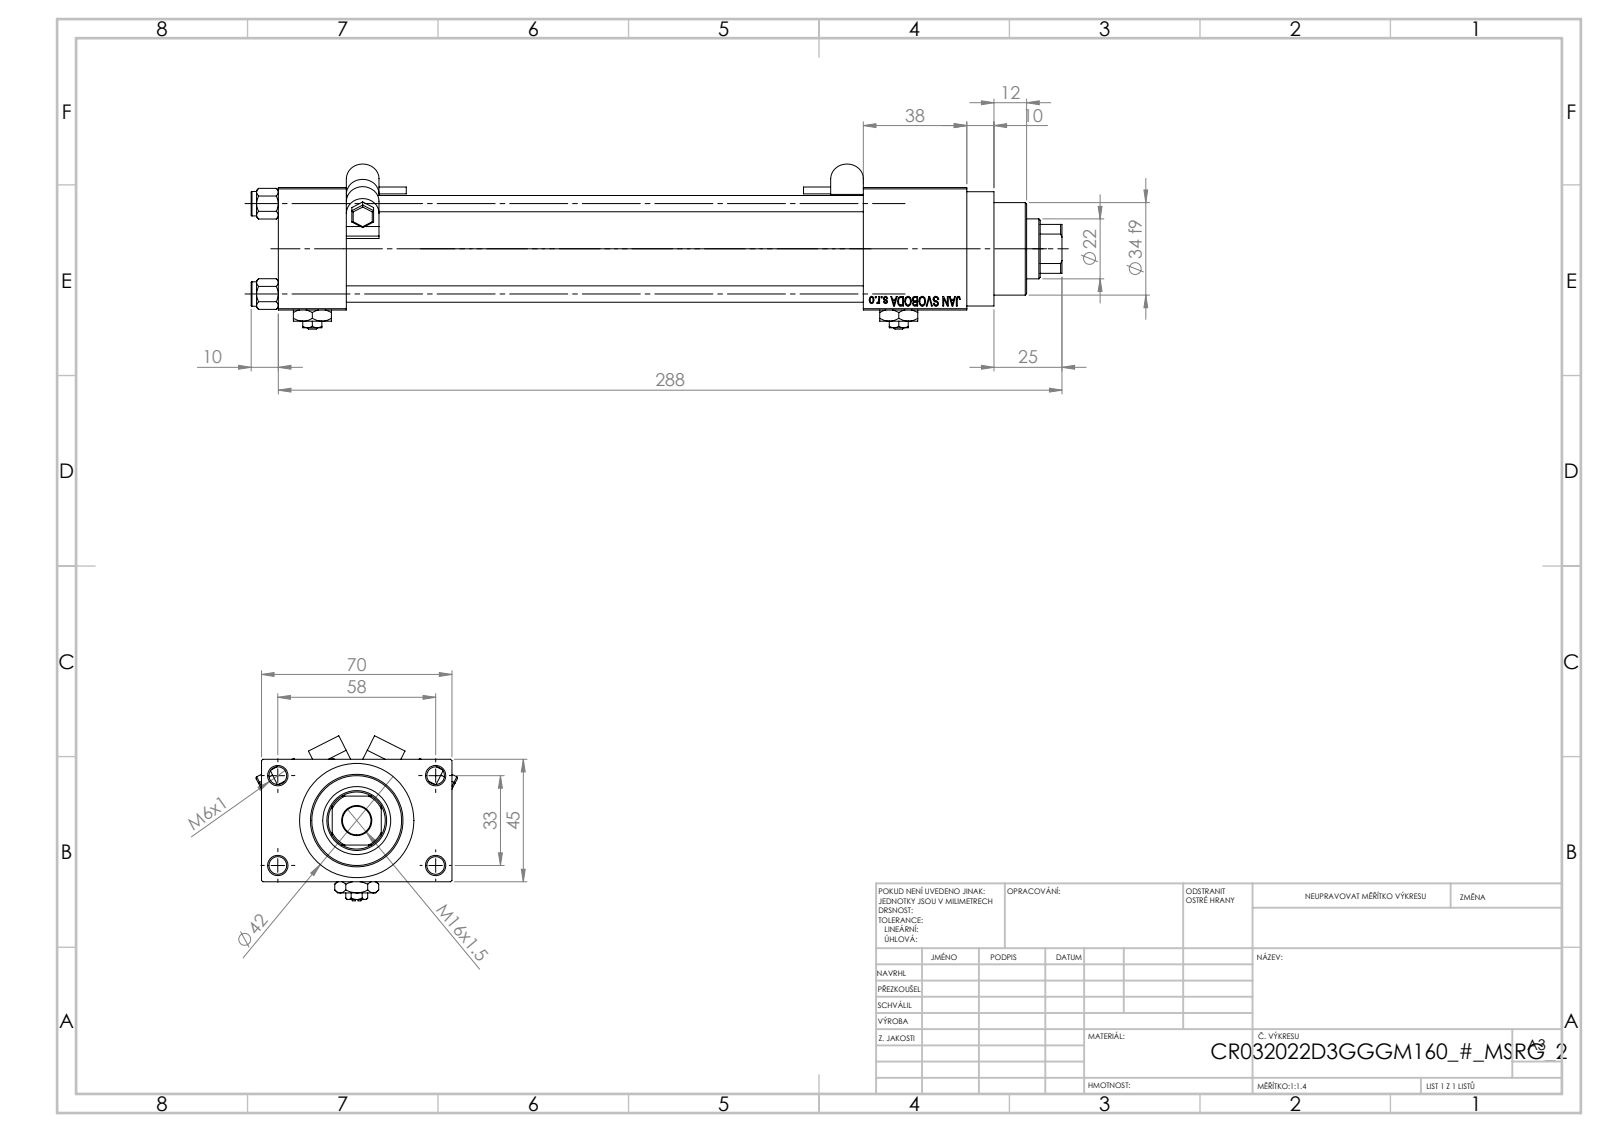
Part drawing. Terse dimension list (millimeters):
name: V215CR_D_TYCINKA; V215CR_VCP_D; MSRF_MSRG1; V215CR_D_Body (+3 more)
written by: SolidWorks 2019 (CONFIG_CONTROL_DESIGN)
unit: mm
bodies: 15 solids, 1266 faces (578 planar, 128 cylindrical, 560 other)
size: 298 × 74.05 × 60.66
volume: 365 555 mm³; area: 136 417 mm²
holes: 4× ⌀6, 4× ⌀6.5, 2× ⌀7, 2× ⌀13.16, 2× ⌀20, 1× ⌀10.5, 1× ⌀22, 1× ⌀24, 1× ⌀25, 1× ⌀32, 1× ⌀33
bosses: 4× ⌀9, 2× ⌀5, 2× ⌀2.5, 1× ⌀42, 1× ⌀38, 1× ⌀34
rounds: 12× R0.5, 4× R6, 1× R10.5
face distances: 45, 25, 12.5, 57.5, 190, 215, 228, 38, 70, 253
hole spacings: 12.4, 23.48, 33.2, 33.37, 35.35, 45.6, 56.35, 33
